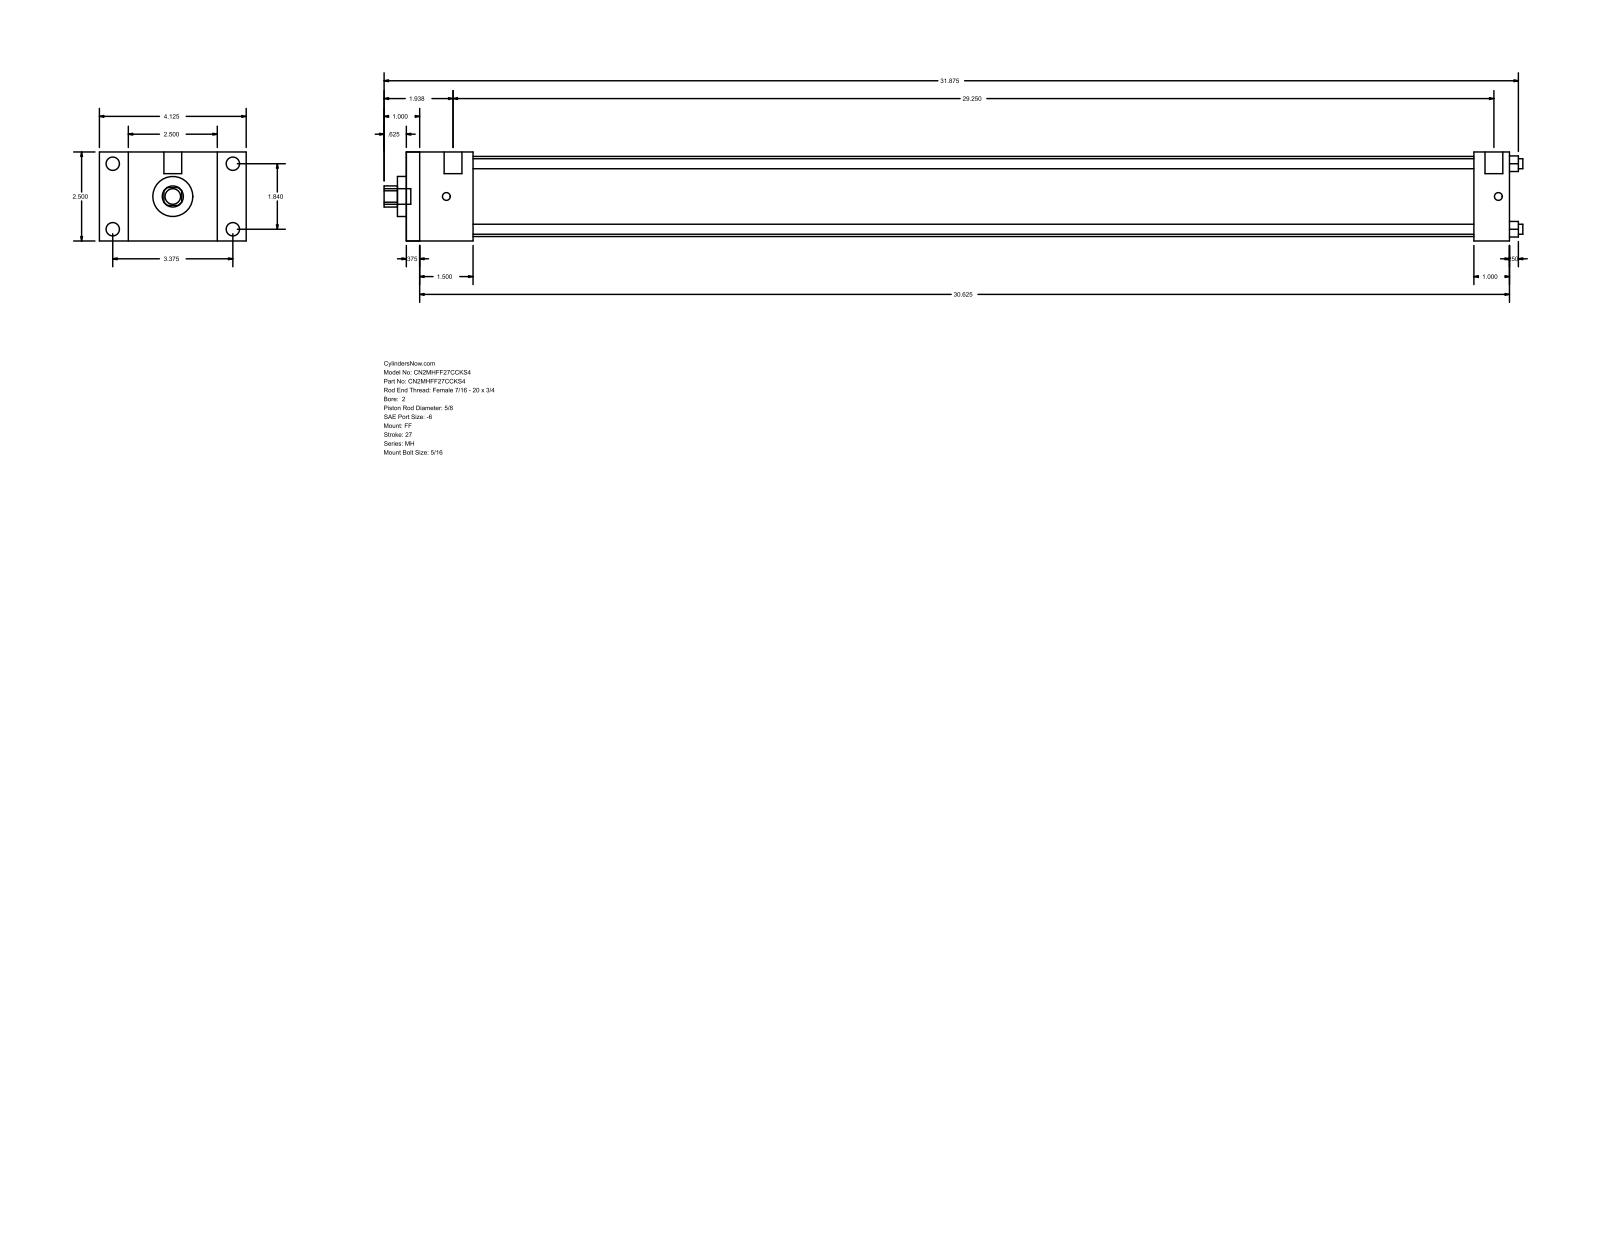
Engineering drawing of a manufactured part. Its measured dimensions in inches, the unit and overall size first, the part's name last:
Units: inches
Overall size (bounding box): 32 × 4.125 × 2.5
Round holes (diameter × count): ⌀0.281 ×4, ⌀0.625 ×1, ⌀1.125 ×1, ⌀2.25 ×1
Round bosses / shafts (diameter × count): ⌀0.375 ×4, ⌀0.219 ×4, ⌀0.5 ×2, ⌀0.437 ×1
Partial cylindrical surfaces — rounded edges, fillets, slot ends (radius × count): R0.297 ×1
Main face-to-face distances: 2.5, 31, 0.375, 30.625, 1.5, 1.875, 30, 29.625, 28.125, 29.125
Hole centre spacings: 1.301, 1.84, 2.602
Bodies: 0 solids, 92 faces (64 planar, 28 cylindrical, 0 other)
Part name (STEP PRODUCT): MH_FF__0200_0.625
STEP written by: GSSL Pune (CONFIG_CONTROL_DESIGN)
